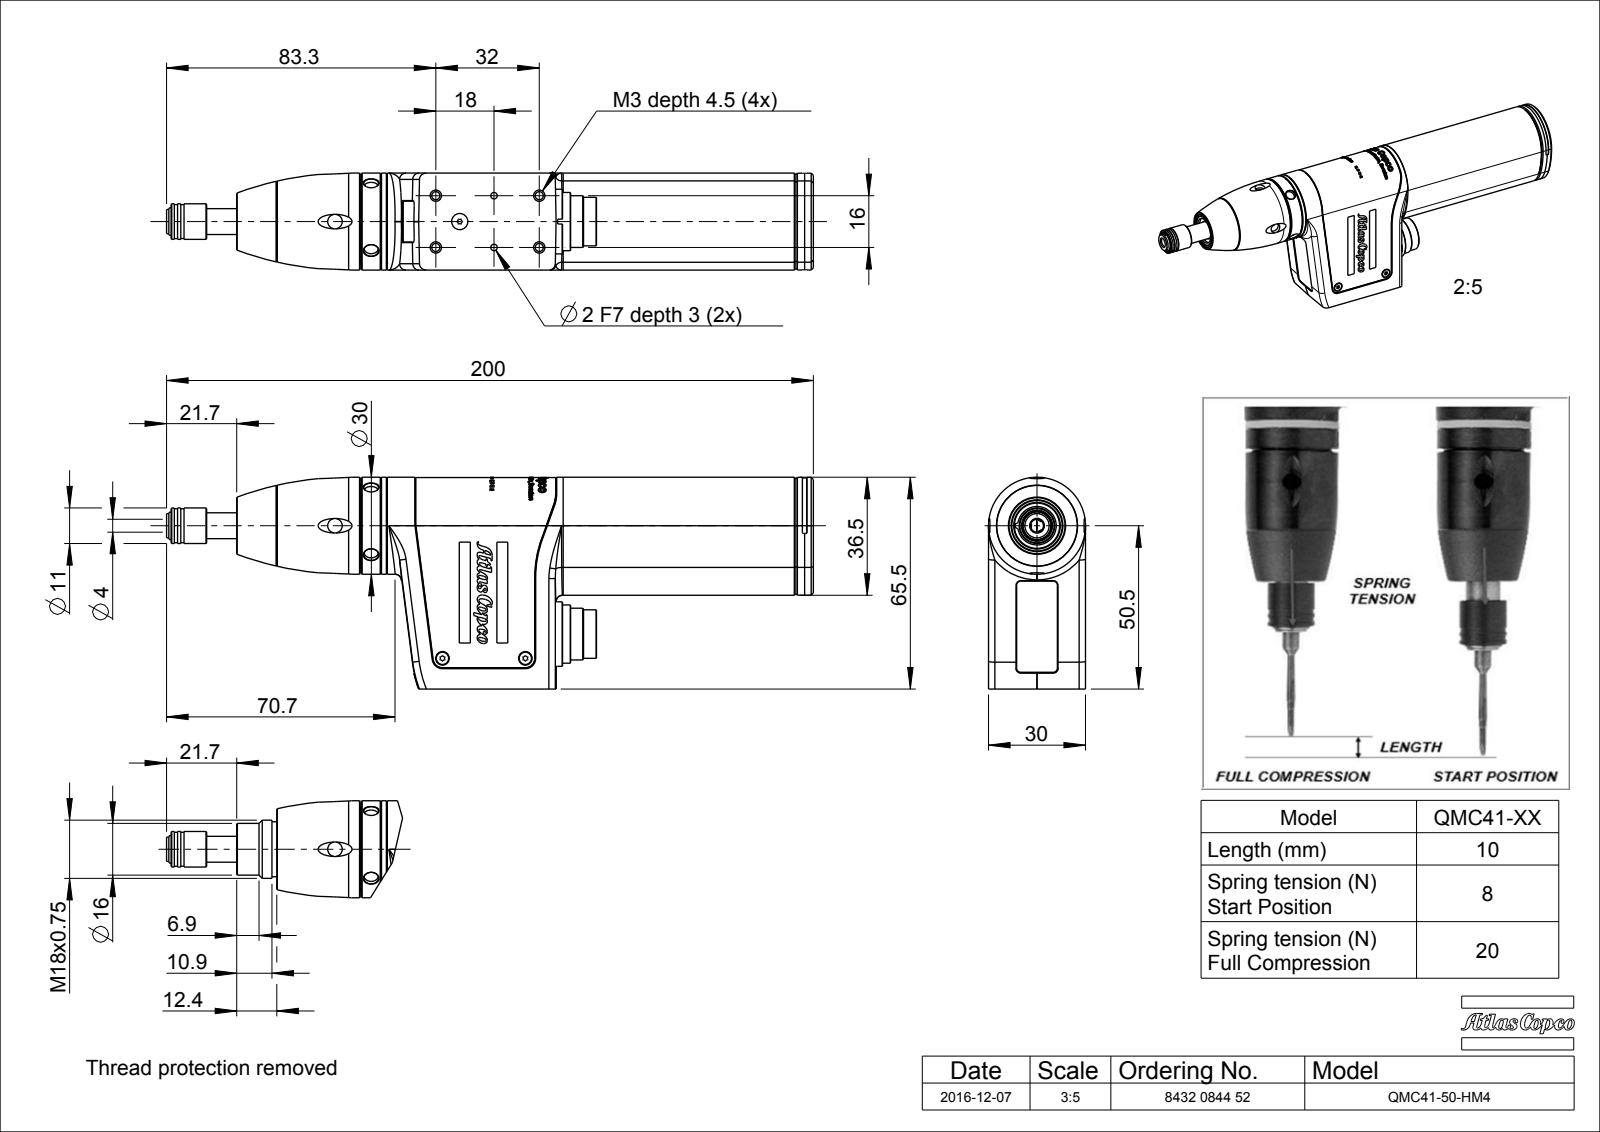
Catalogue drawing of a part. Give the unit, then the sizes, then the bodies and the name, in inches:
Units: inches
Overall size (bounding box): 7.878 × 2.579 × 1.181
Round holes (diameter × count): ⌀0.024 ×12, ⌀0.079 ×6, ⌀0.177 ×6, ⌀0.063 ×4, ⌀0.098 ×4, ⌀0.067 ×3, ⌀0.083 ×3, ⌀0.087 ×3, ⌀0.039 ×2, ⌀0.047 ×2, ⌀0.081 ×2, ⌀0.106 ×2
Round bosses / shafts (diameter × count): ⌀0.039 ×12, ⌀0.028 ×12, ⌀0.024 ×12, ⌀0.15 ×5, ⌀0.079 ×3, ⌀0.787 ×2, ⌀0.709 ×2, ⌀1.181 ×1
Partial cylindrical surfaces — rounded edges, fillets, slot ends (radius × count): R0.079 ×36, R0.008 ×28, R0.004 ×18, R0.007 ×12, R0.013 ×12, R0.021 ×12, R0.016 ×8, R0.059 ×8
Main face-to-face distances: 0.028, 1.146, 1.173, 1.118, 0.031, 1.15, 1.177, 0.079, 1.181, 0.462
Hole centre spacings: 0.63, 0.083, 0.106, 0.122, 0.137, 0.234, 0.263, 0.689
Volume: 3.761 in³ · Surface area: 101.2 in²
Bodies: 24 solids, 1577 faces (390 planar, 682 cylindrical, 505 other)
Part name (STEP PRODUCT): 4216253400; 4216253600; 4216256600; NG_FLEX_AF8 (+8 more)
STEP written by: CREO PARAMETRIC BY PTC INC, 2016260 (CONFIG_CONTROL_DESIGN)
